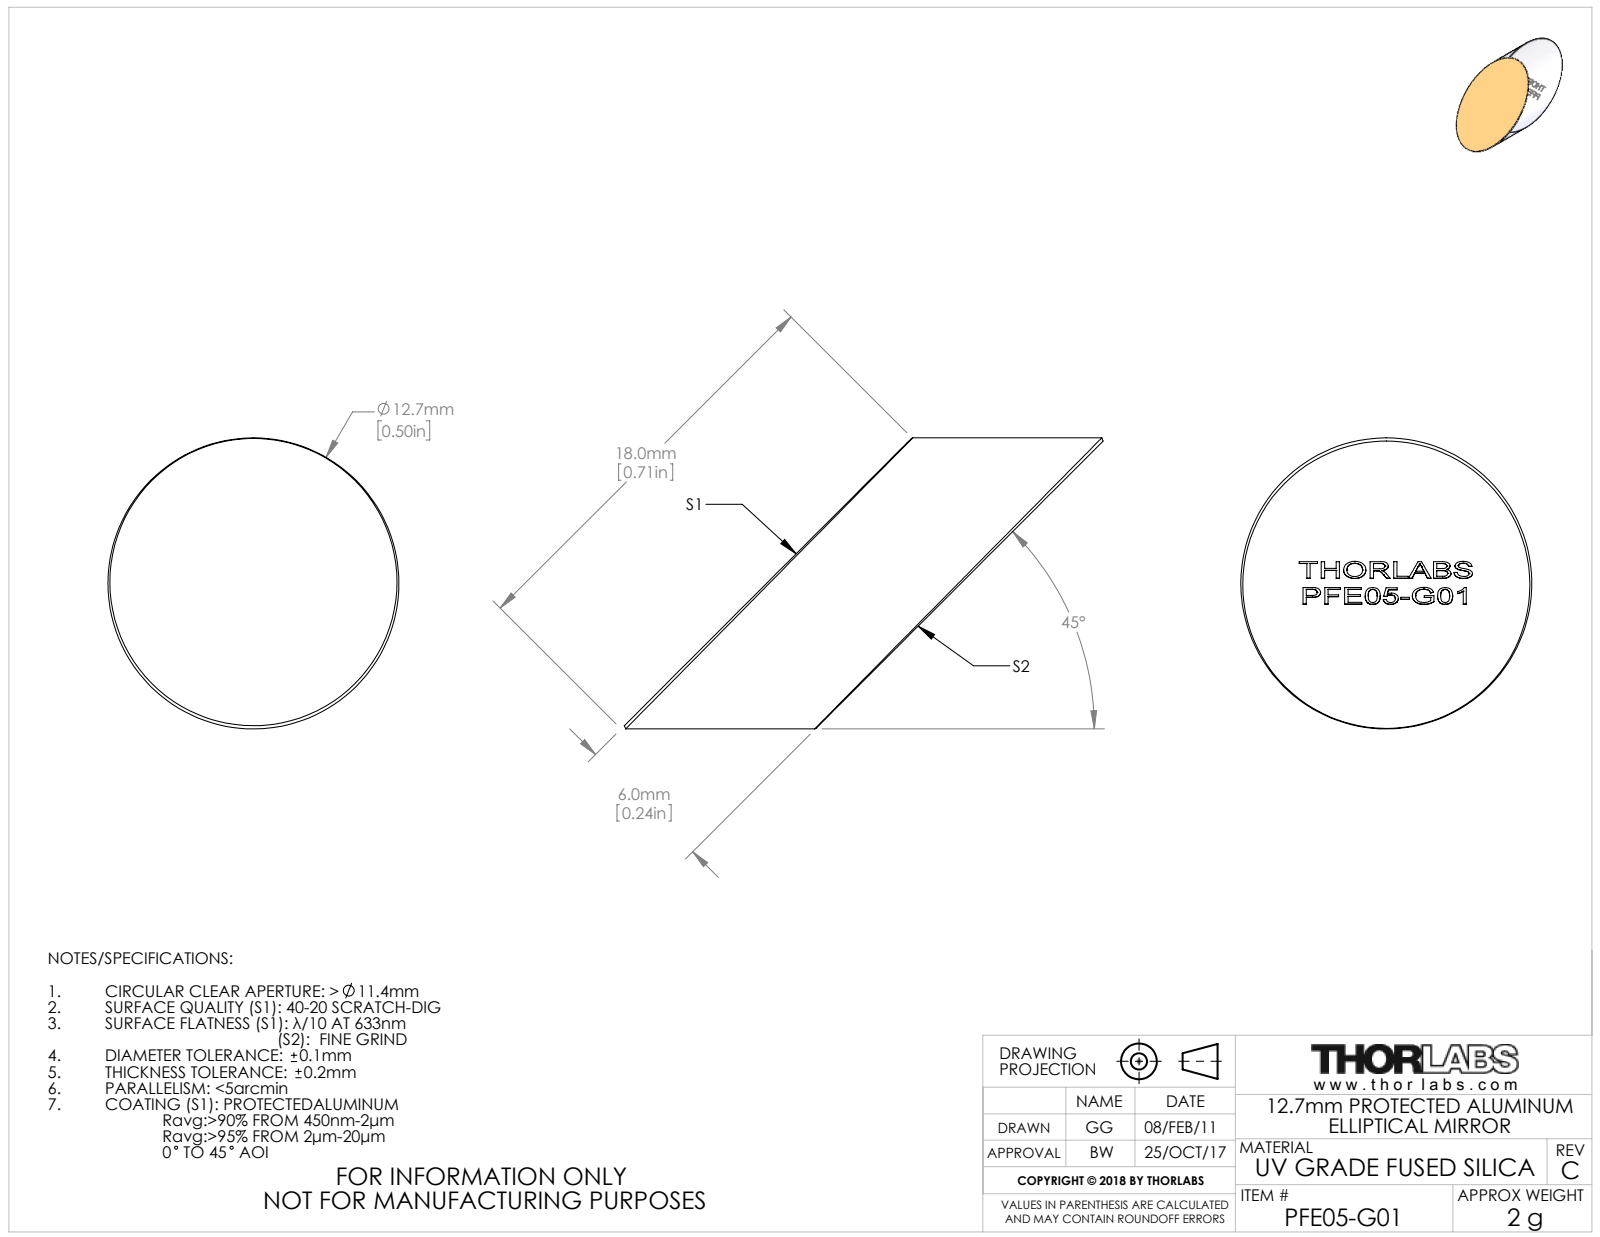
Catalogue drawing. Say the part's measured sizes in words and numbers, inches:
The part is named "21935-E0W". Its 3-D file was written by "SolidWorks 2016 (CONFIG_CONTROL_DESIGN)". It is 1 solid with 232 faces: 138 planar, 2 cylindrical and 92 other. Overall it measures 0.823 by 0.5 by 0.5 inches. Its volume is 0.066 cubic inches and its surface area 1.068 square inches. Round bosses or shafts: 1 of diameter 0.5. The main face-to-face distances are 0.236, 0.063, 0.041, 0.036, 0.04, 0.031, 0.05, 0.019, 0.084, 0.099.
